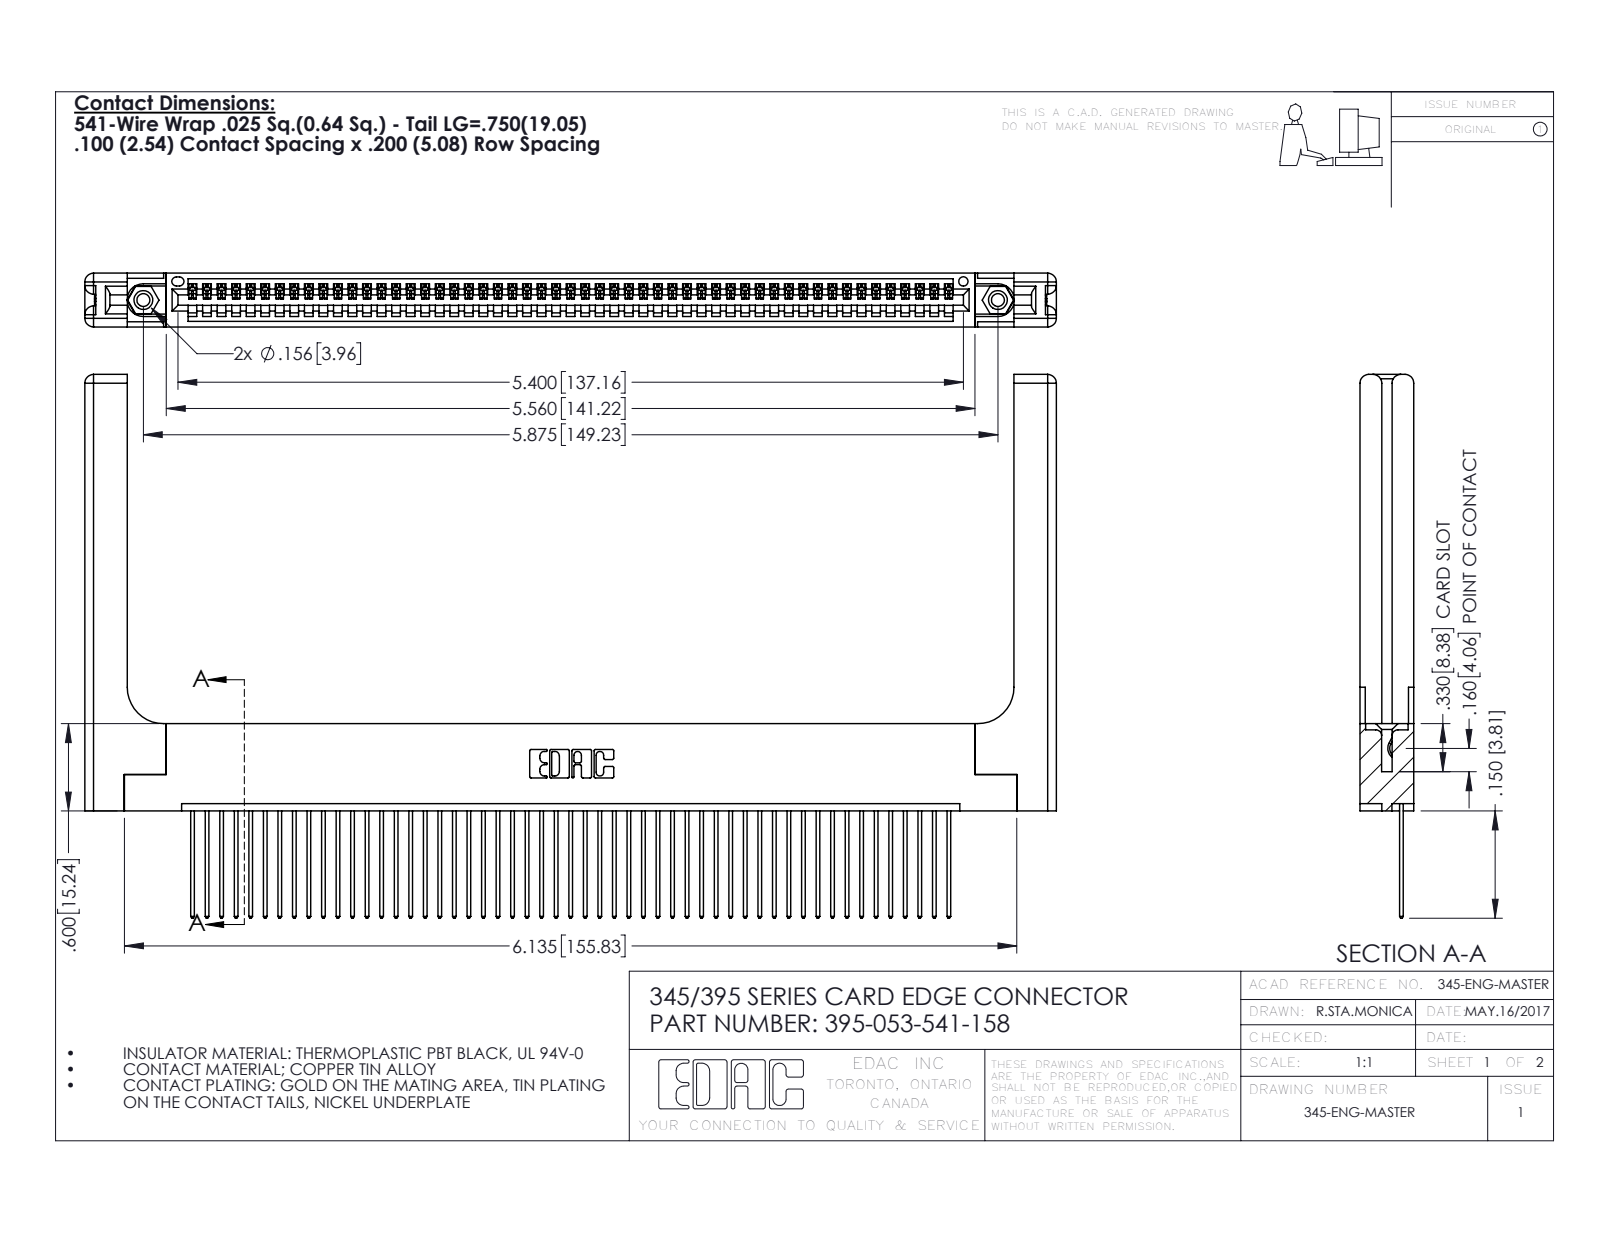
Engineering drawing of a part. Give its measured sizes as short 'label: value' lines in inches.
name: 345-250-001_345-250-001-102; 345 Part_Flush Mounting Lugs - 0.156 Dia-TH; 395-053-541-158; 345-292-001_345-293-141 (+1 more)
written by: SolidWorks 2016 (CONFIG_CONTROL_DESIGN)
unit: in
bodies: 58 solids, 3456 faces (2348 planar, 1048 cylindrical, 60 other)
size: 6.679 × 3.737 × 0.37
volume: 1.518 in³; area: 43.79 in²
holes: 2× ⌀0.089, 2× ⌀0.125, 2× ⌀0.156, 1× ⌀0.064
bosses: 2× ⌀0.155
rounds: 106× R0.006, 106× R0.01, 22× R0.01, 16× R0.06, 6× R0.007, 6× R0.031, 3× R0.026, 2× R0.03
face distances: 0.072, 0.298, 0.37, 0.098, 0.272, 0.025, 0.2, 0.225, 0.148, 0.15
hole spacings: 0.27, 5.639, 5.875
